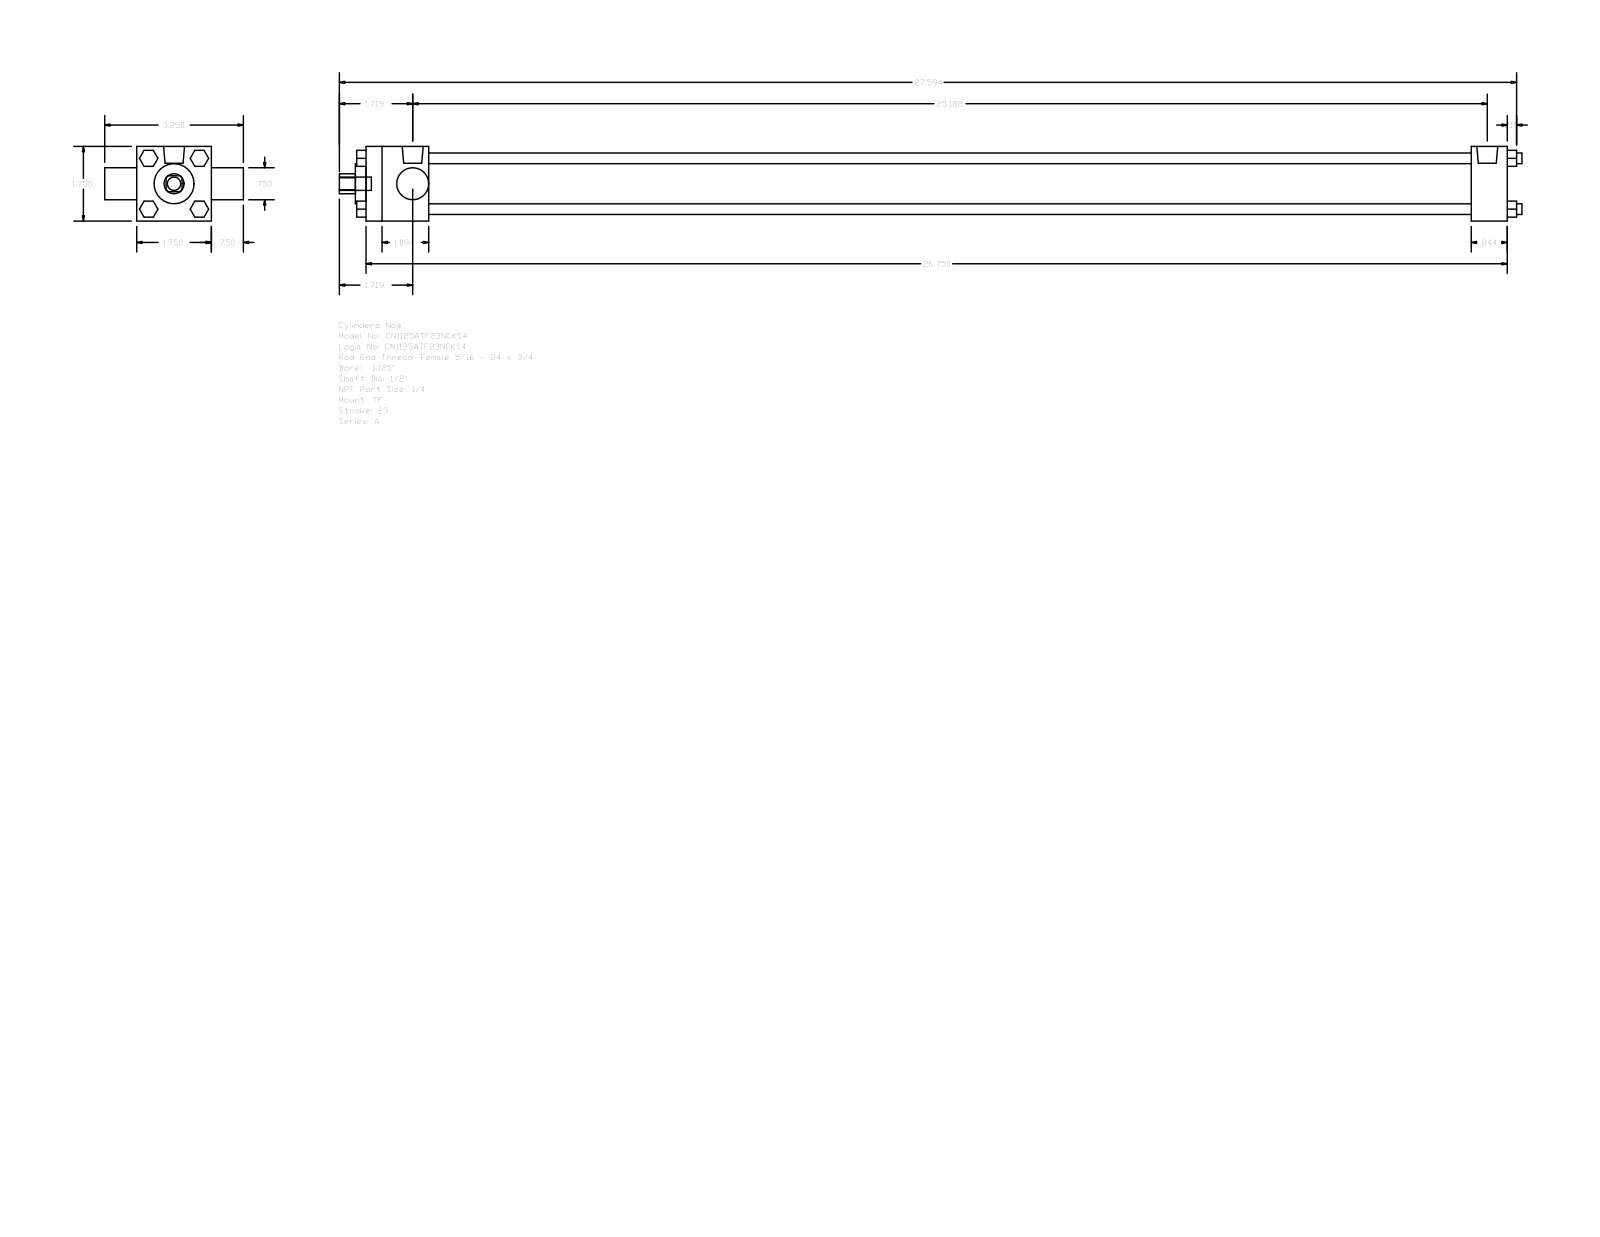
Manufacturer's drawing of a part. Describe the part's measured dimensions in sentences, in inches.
The part is named "A_TF__0112_0.5". Its 3-D file was written by "GSSL Pune (CONFIG_CONTROL_DESIGN)". It is 0 solids with 120 faces: 92 planar, 28 cylindrical and 0 other. Overall it measures 27.719 by 3.25 by 1.75 inches. Round holes: 1 of diameter 0.5, 1 of diameter 0.75, 1 of diameter 0.937, 1 of diameter 1.255. Round bosses or shafts: 4 of diameter 0.25, 3 of diameter 0.219, 2 of diameter 0.492, 1 of diameter 0.313. Partial cylindrical surfaces (rounded edges, fillets, slot ends): 1 of radius 0.234. The main face-to-face distances are 1.75, 26.75, 25.906, 0.844, 1.469, 24.437, 25.281, 0.75, 2.5, 0.375.
